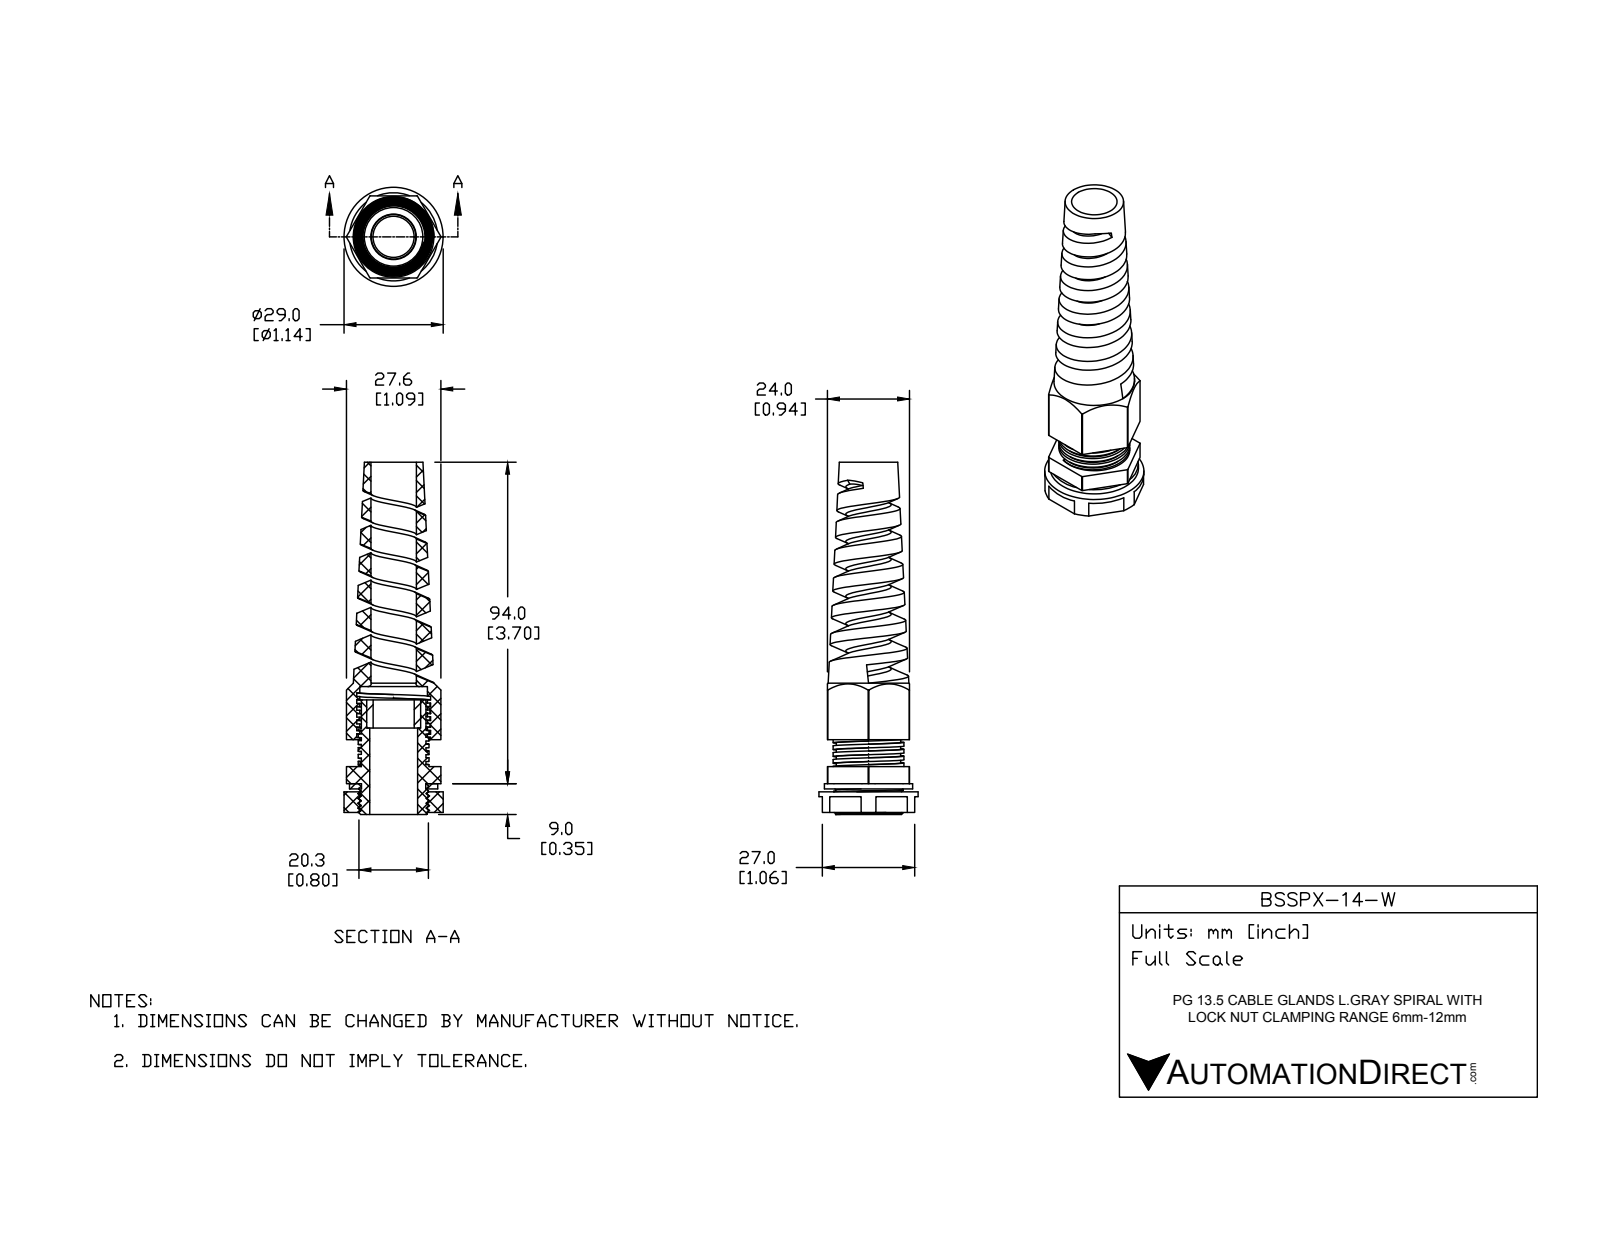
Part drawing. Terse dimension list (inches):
name: BSSPX-14-W
written by: SolidWorks 2015 (CONFIG_CONTROL_DESIGN)
unit: in
bodies: 5 solids, 237 faces (105 planar, 96 cylindrical, 36 other)
size: 4.055 × 1.142 × 1.142
volume: 1.188 in³; area: 30.84 in²
holes: 1× ⌀0.472, 1× ⌀0.524, 1× ⌀0.551, 1× ⌀0.622, 1× ⌀0.74, 1× ⌀0.773, 1× ⌀0.779
bosses: 1× ⌀1.142, 1× ⌀1.016, 1× ⌀0.815, 1× ⌀0.799, 1× ⌀0.744
rounds: 1× R0.543
face distances: 0.945, 0.059, 0.094, 0.236, 0.33, 1.004, 0.271, 0.035, 0.527, 0.291
